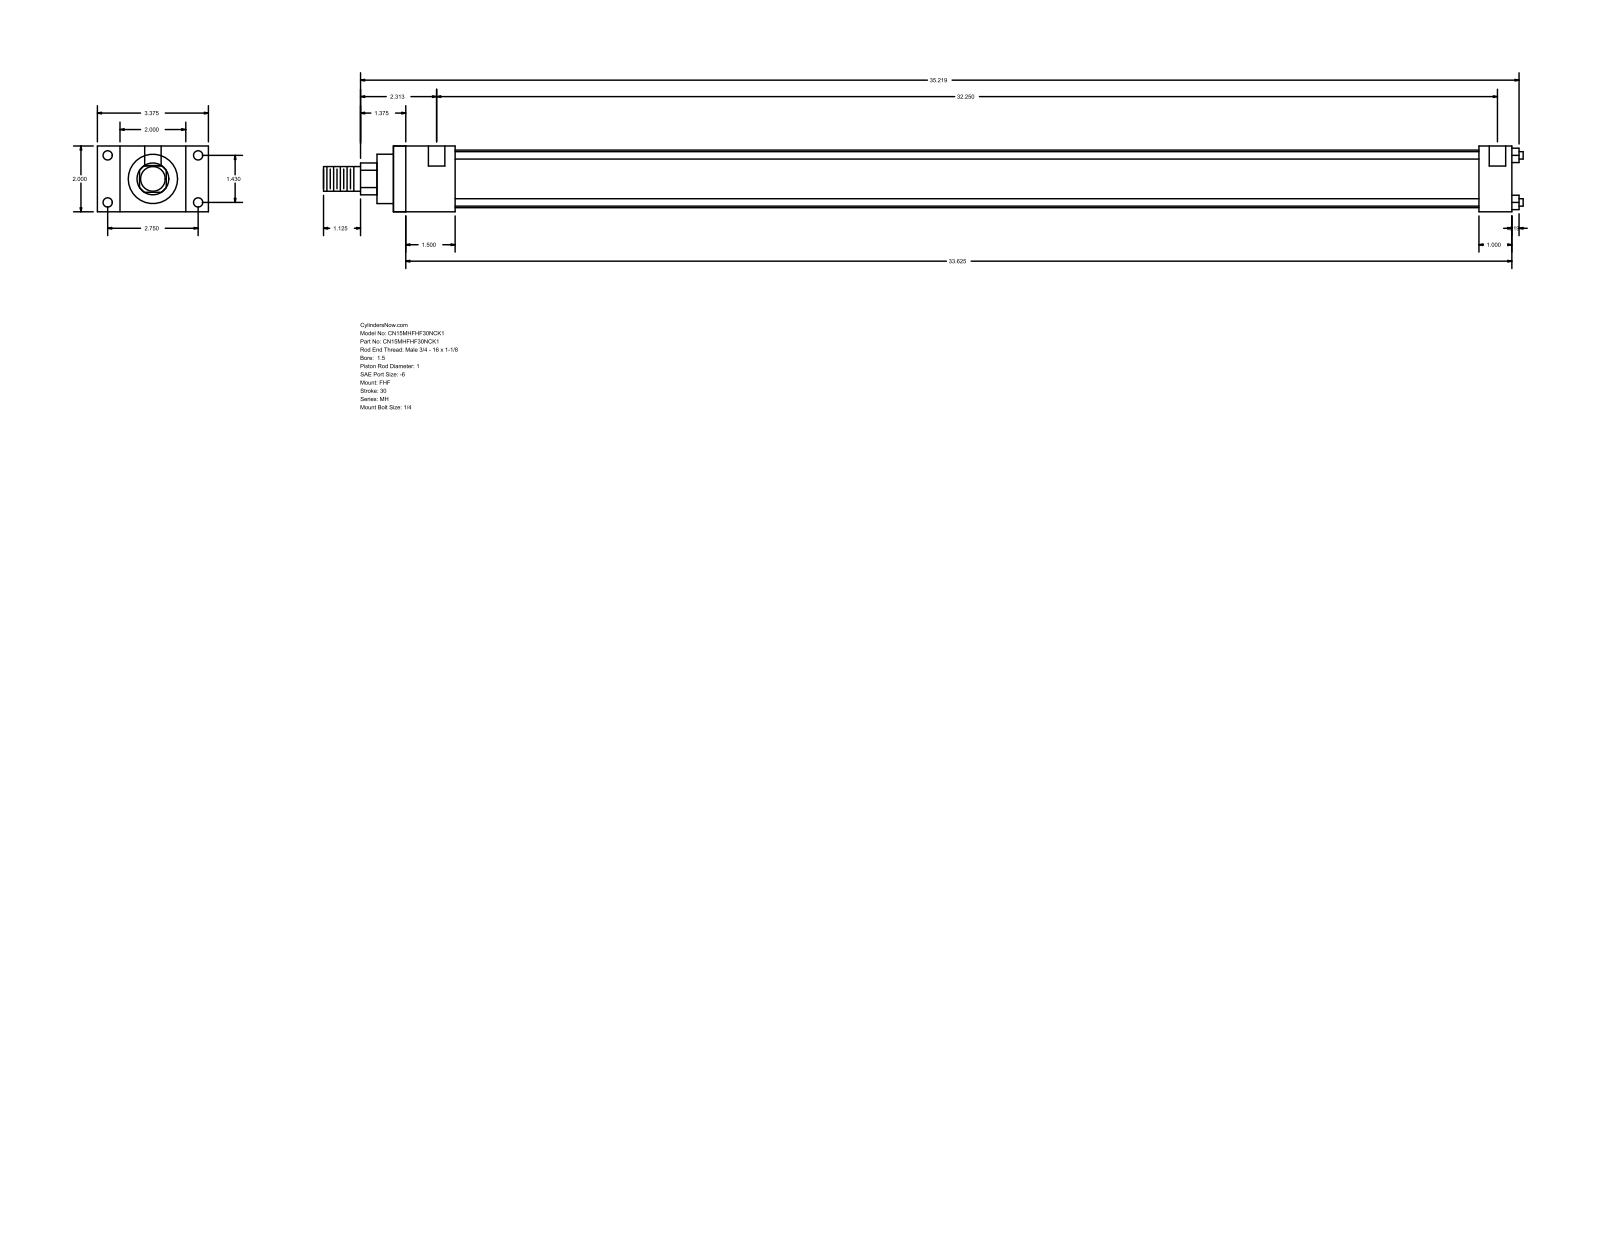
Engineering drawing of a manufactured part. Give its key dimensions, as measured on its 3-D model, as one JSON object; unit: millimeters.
{"part_name": "MH_FHF__0150_1", "step_written_by": "GSSL Pune (CONFIG_CONTROL_DESIGN)", "units": "millimeters", "bodies": {"solids": 0, "faces": 88, "planar": 60, "cylindrical": 28, "other": 0}, "overall_size": [926.31, 85.72, 50.8], "round_holes": [[5.56, 4], [7.14, 4], [12.7, 2]], "round_bosses_or_shafts": [[5.71, 4], [44.45, 1], [38.1, 1], [25.4, 1], [19.05, 1]], "partial_cylinders_radius": [[12.29, 1]], "face_to_face_distances": [50.8, 17.46, 68.26, 47.63, 85.72, 863.6, 815.97, 25.4, 838.2, 790.57], "hole_center_spacings": [36.32, 69.84, 78.72, 822.33, 3.18, 819.15]}
